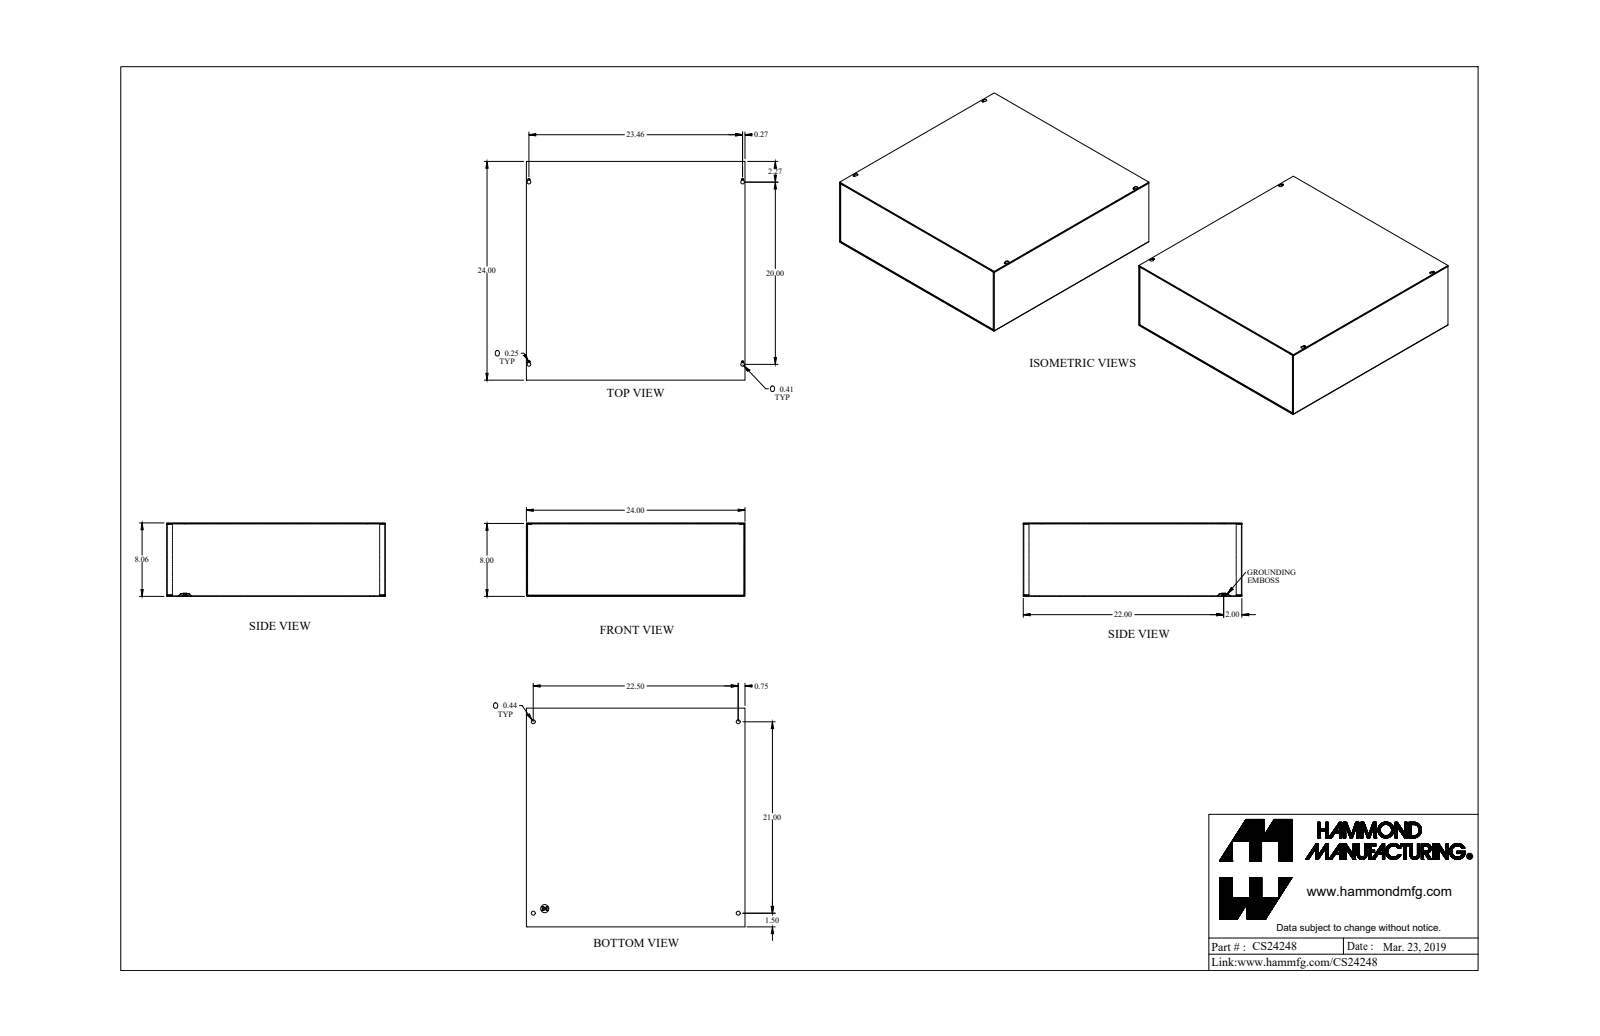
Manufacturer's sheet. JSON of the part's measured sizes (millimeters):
{"part_name": "CS24248_Default", "step_written_by": "SolidWorks 2019 (CONFIG_CONTROL_DESIGN)", "units": "millimeters", "bodies": {"solids": 4, "faces": 205, "planar": 125, "cylindrical": 72, "other": 8}, "overall_size": [609.6, 609.6, 204.6], "volume_mm3": 1860000, "surface_area_mm2": 2583000, "round_holes": [[4.3, 5], [11.1, 4], [12.7, 1]], "round_bosses_or_shafts": [[12.5, 1], [7.2, 1]], "partial_cylinders_radius": [[0.7, 12], [2.2, 12], [1.4, 8], [3.2, 4], [5.2, 4]], "face_to_face_distances": [1.4, 203.2, 608.2, 201.8, 204.6, 609.6, 606.7, 2, 199.7, 201.2], "hole_center_spacings": [17.6, 520.9, 583.8, 782.2, 508, 533.4, 571.5, 595.9]}
